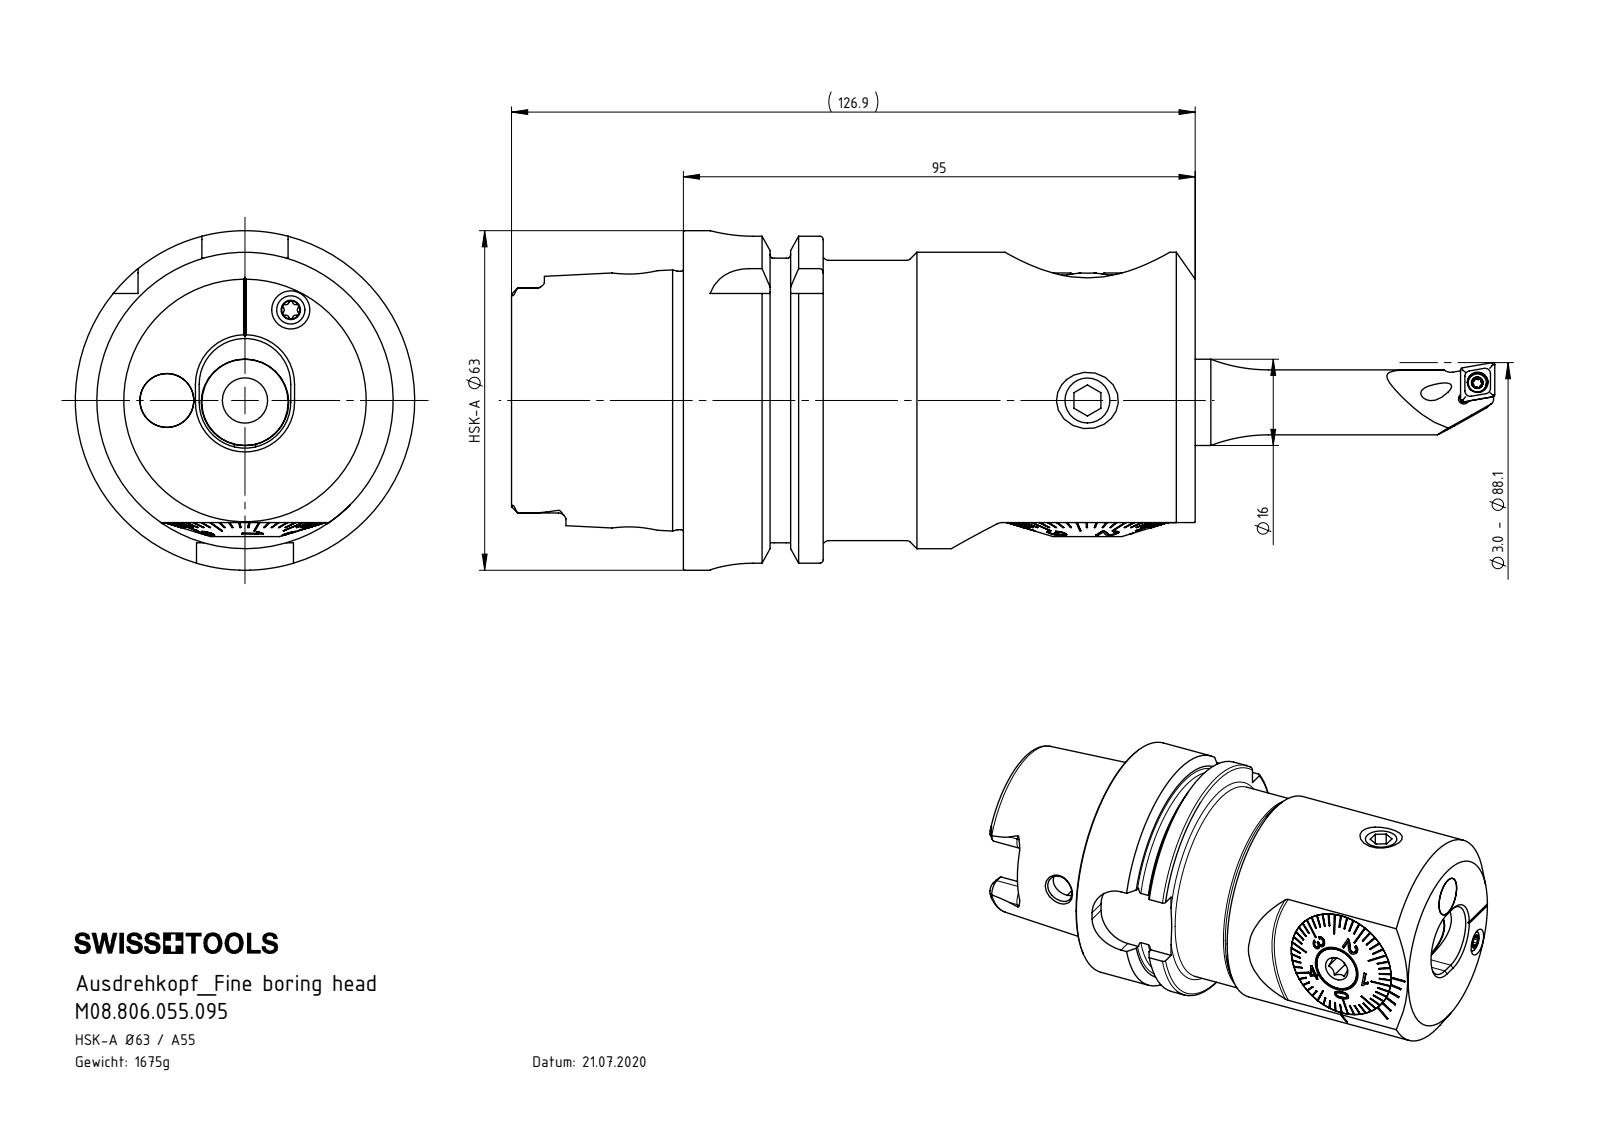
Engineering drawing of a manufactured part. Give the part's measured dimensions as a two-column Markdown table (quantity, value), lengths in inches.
| quantity | value |
| --- | --- |
| part name | A55-BG1.DA3.041_A; ISO 4026 - M10 x 16_PreviewCfg; A55-BG2.012.006_B; WCB-ER2.001.009_A (+8 more) |
| STEP written by | SolidWorks 2017 (AUTOMOTIVE_DESIGN) |
| units | inches |
| bodies | 16 solids, 718 faces (367 planar, 116 cylindrical, 235 other) |
| overall size | 4.996 × 2.48 × 2.48 |
| volume | 12.95 in³ |
| surface area | 88.24 in² |
| round holes (diameter × count) | 0.335 × 3, 0.394 × 2, 0.063 × 1, 0.13 × 1, 0.165 × 1, 0.295 × 1, 0.315 × 1, 0.331 × 1, 0.449 × 1, 0.488 × 1, 0.551 × 1, 0.559 × 1 |
| round bosses / shafts (diameter × count) | 0.394 × 3, 2.48 × 1, 2.165 × 1, 2.163 × 1, 2.047 × 1, 1.887 × 1, 1.181 × 1, 1.18 × 1 |
| partial cylindrical surfaces (radius × count) | 0.055 × 10, 0.013 × 6, 0.023 × 6, 0.02 × 4, 0.031 × 4, 0.075 × 4, 0.113 × 4, 0.315 × 4 |
| main face-to-face distances | 3.74, 0.63, 1.022, 2.719, 0.209, 0.392, 3.348, 0.256, 0.11, 0.098 |
| hole center spacings | 0.571, 0.285, 0.014, 0.741, 0.754, 1.121, 2.677, 3.022 |
